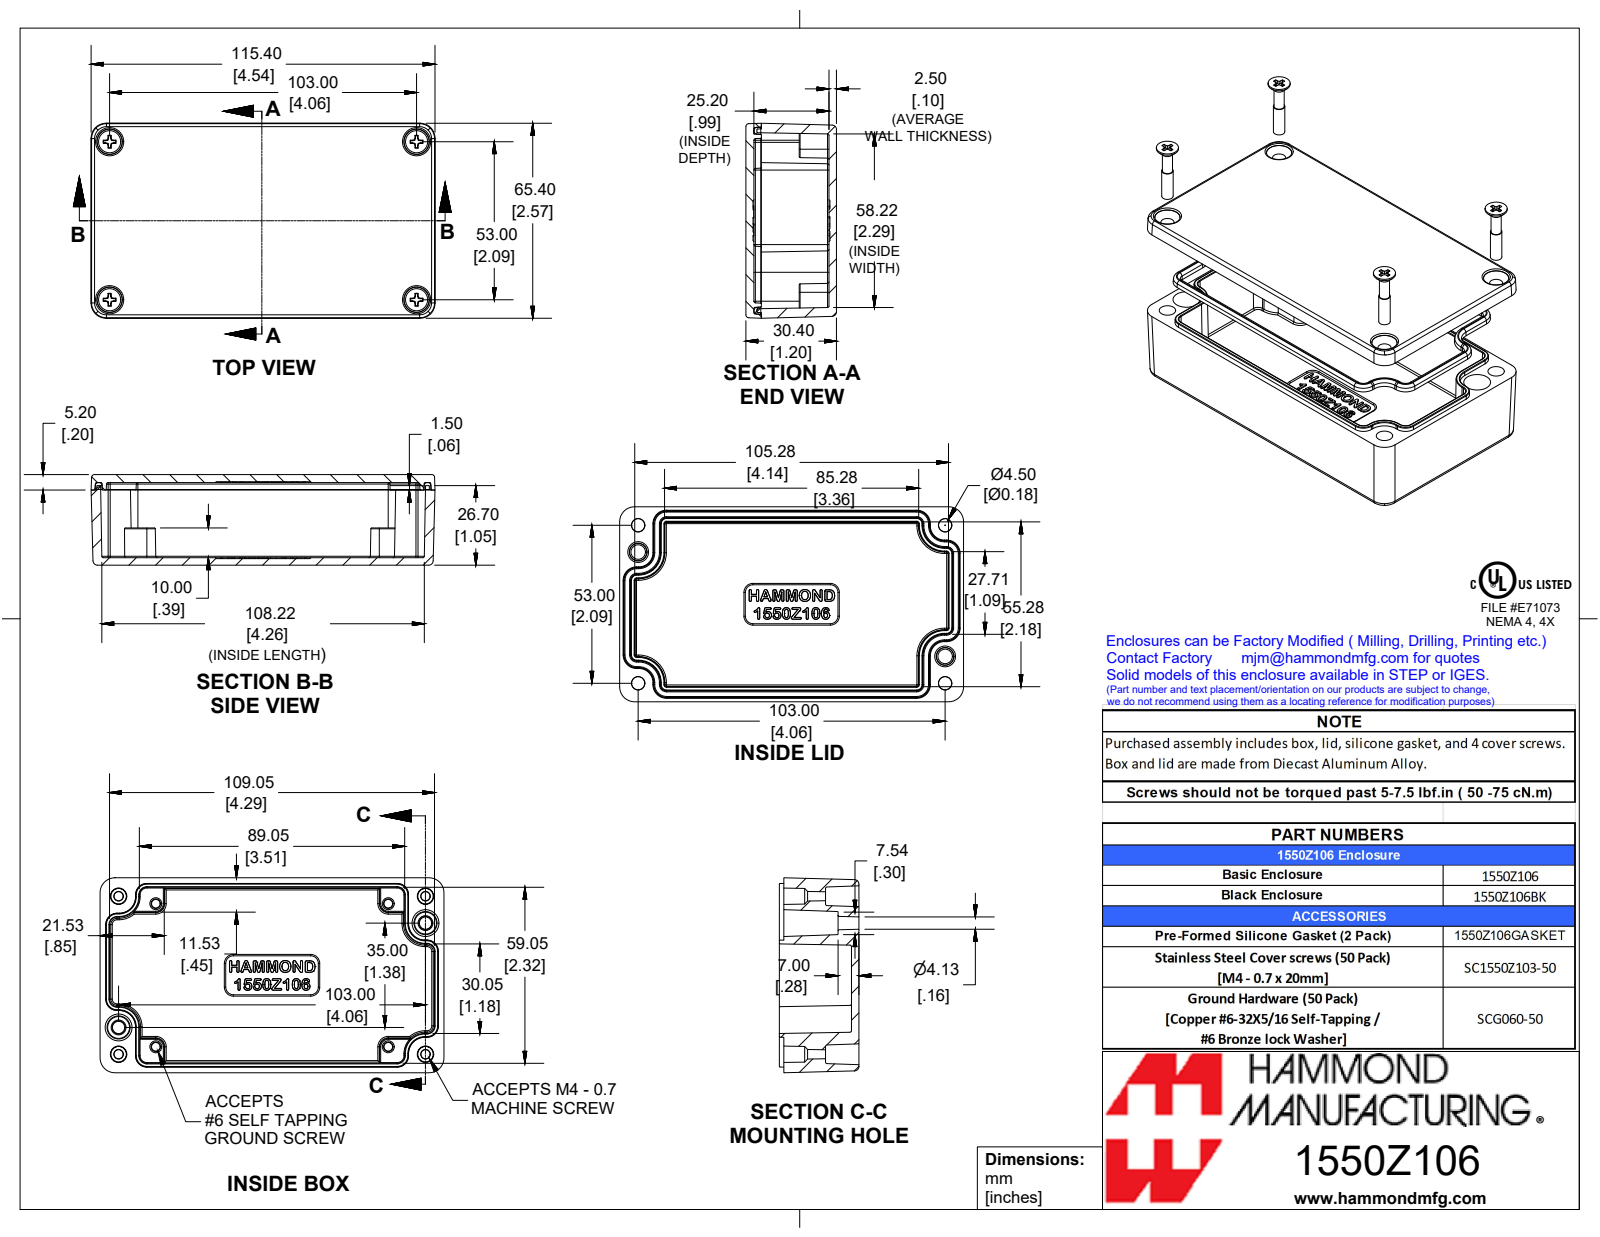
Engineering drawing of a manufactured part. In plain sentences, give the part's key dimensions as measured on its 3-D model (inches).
The part is named "1550Z106". Its 3-D file was written by "SolidWorks 2019 (AUTOMOTIVE_DESIGN)". It is 7 solids with 1397 faces: 377 planar, 238 cylindrical and 782 other. Overall it measures 4.543 by 2.575 by 1.197 inches. Its volume is 4.776 cubic inches and its surface area 89.34 square inches. Round bosses or shafts: 4 of diameter 0.299, 4 of diameter 0.154, 4 of diameter 0.13. Partial cylindrical surfaces (rounded edges, fillets, slot ends): 50 of radius 0.008, 32 of radius 0.02, 24 of radius 0.012, 24 of radius 0.039, 8 of radius 0.197, 4 of radius 0.059. The main face-to-face distances are 0.098, 0.992, 1.197, 1.091, 0.106, 1.098, 0.894, 0.205, 0.197, 0.091.
